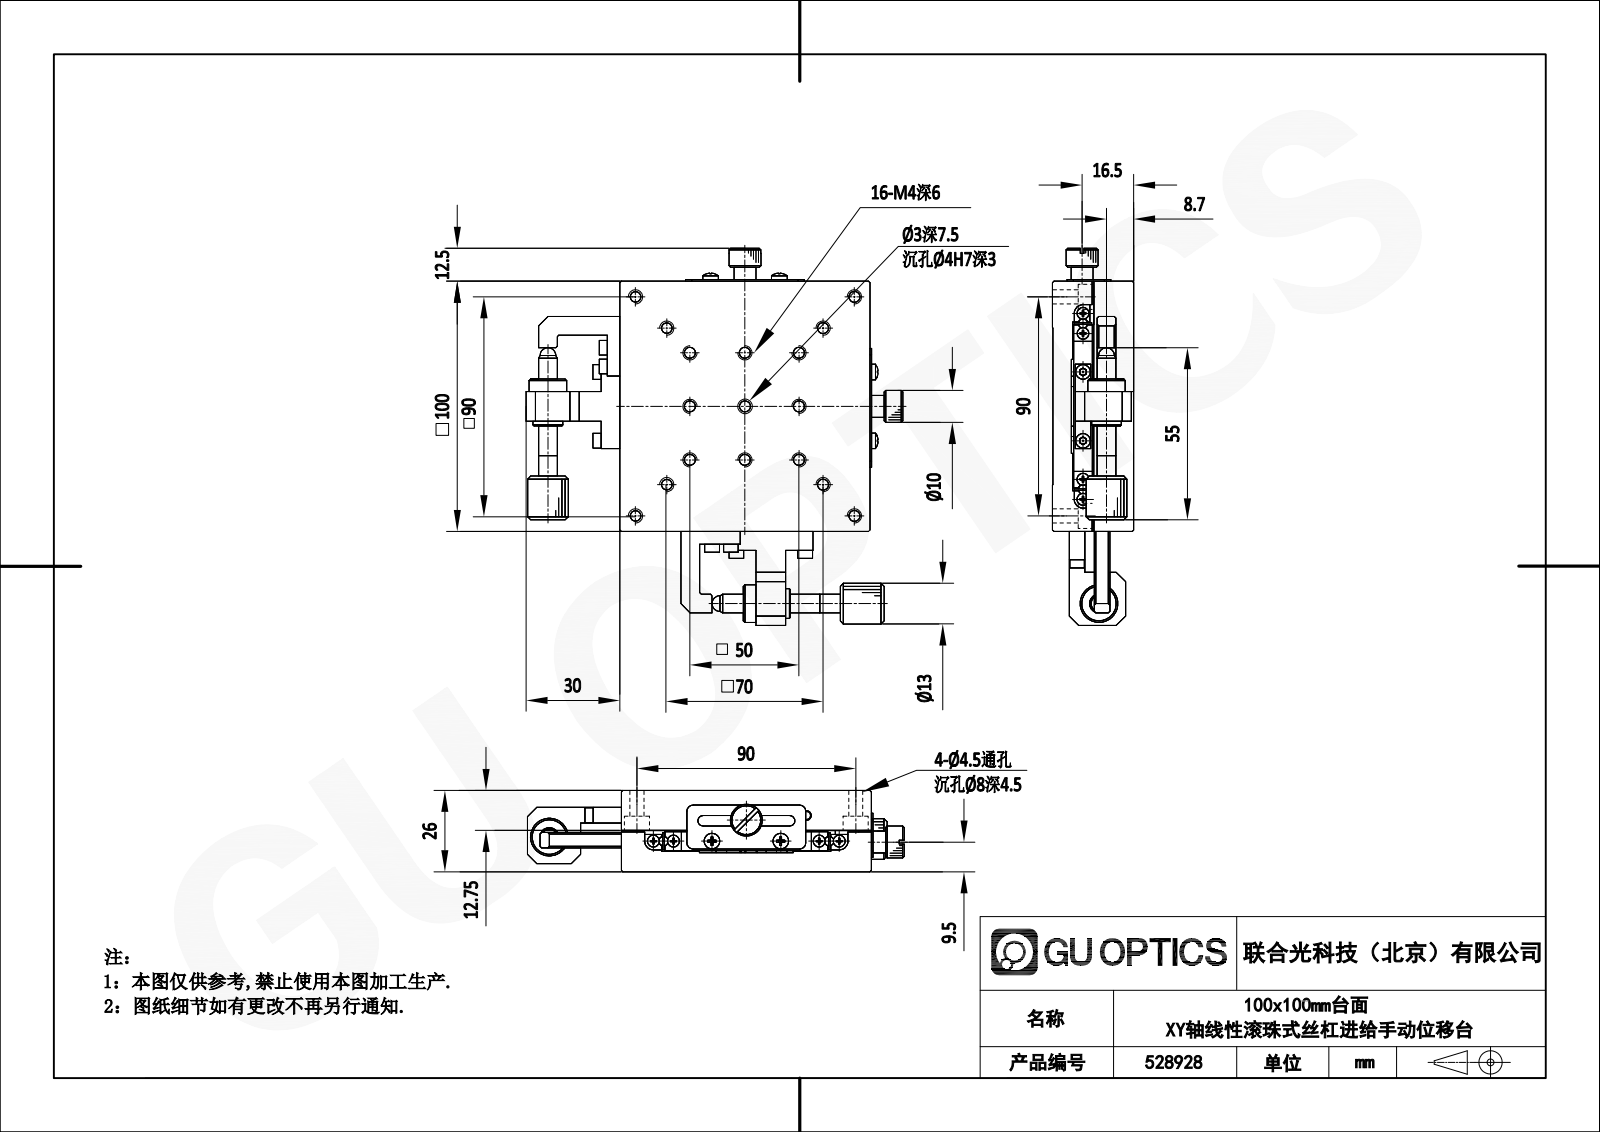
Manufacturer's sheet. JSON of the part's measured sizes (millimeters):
{"part_name": "528928", "step_written_by": "SolidWorks 2020 (CONFIG_CONTROL_DESIGN)", "units": "millimeters", "bodies": {"solids": 0, "faces": 1360, "planar": 752, "cylindrical": 428, "other": 180}, "overall_size": [141.8, 141.8, 26], "round_holes": [[3, 4], [2.8, 2], [7, 1]], "round_bosses_or_shafts": [[2.05, 29], [3.24, 16], [2.8, 6], [8, 4], [6, 4], [4.5, 4], [2.5, 3], [12, 2]], "partial_cylinders_radius": [[1.75, 16], [2, 8], [1.65, 4], [3, 4], [5, 2], [6.5, 2]], "face_to_face_distances": [6.5, 13, 6.25, 0.5, 19.5, 7, 6, 19, 12.5, 5.75], "hole_center_spacings": [12.78, 22, 6, 6.58, 9.55, 23.9, 29.72]}
